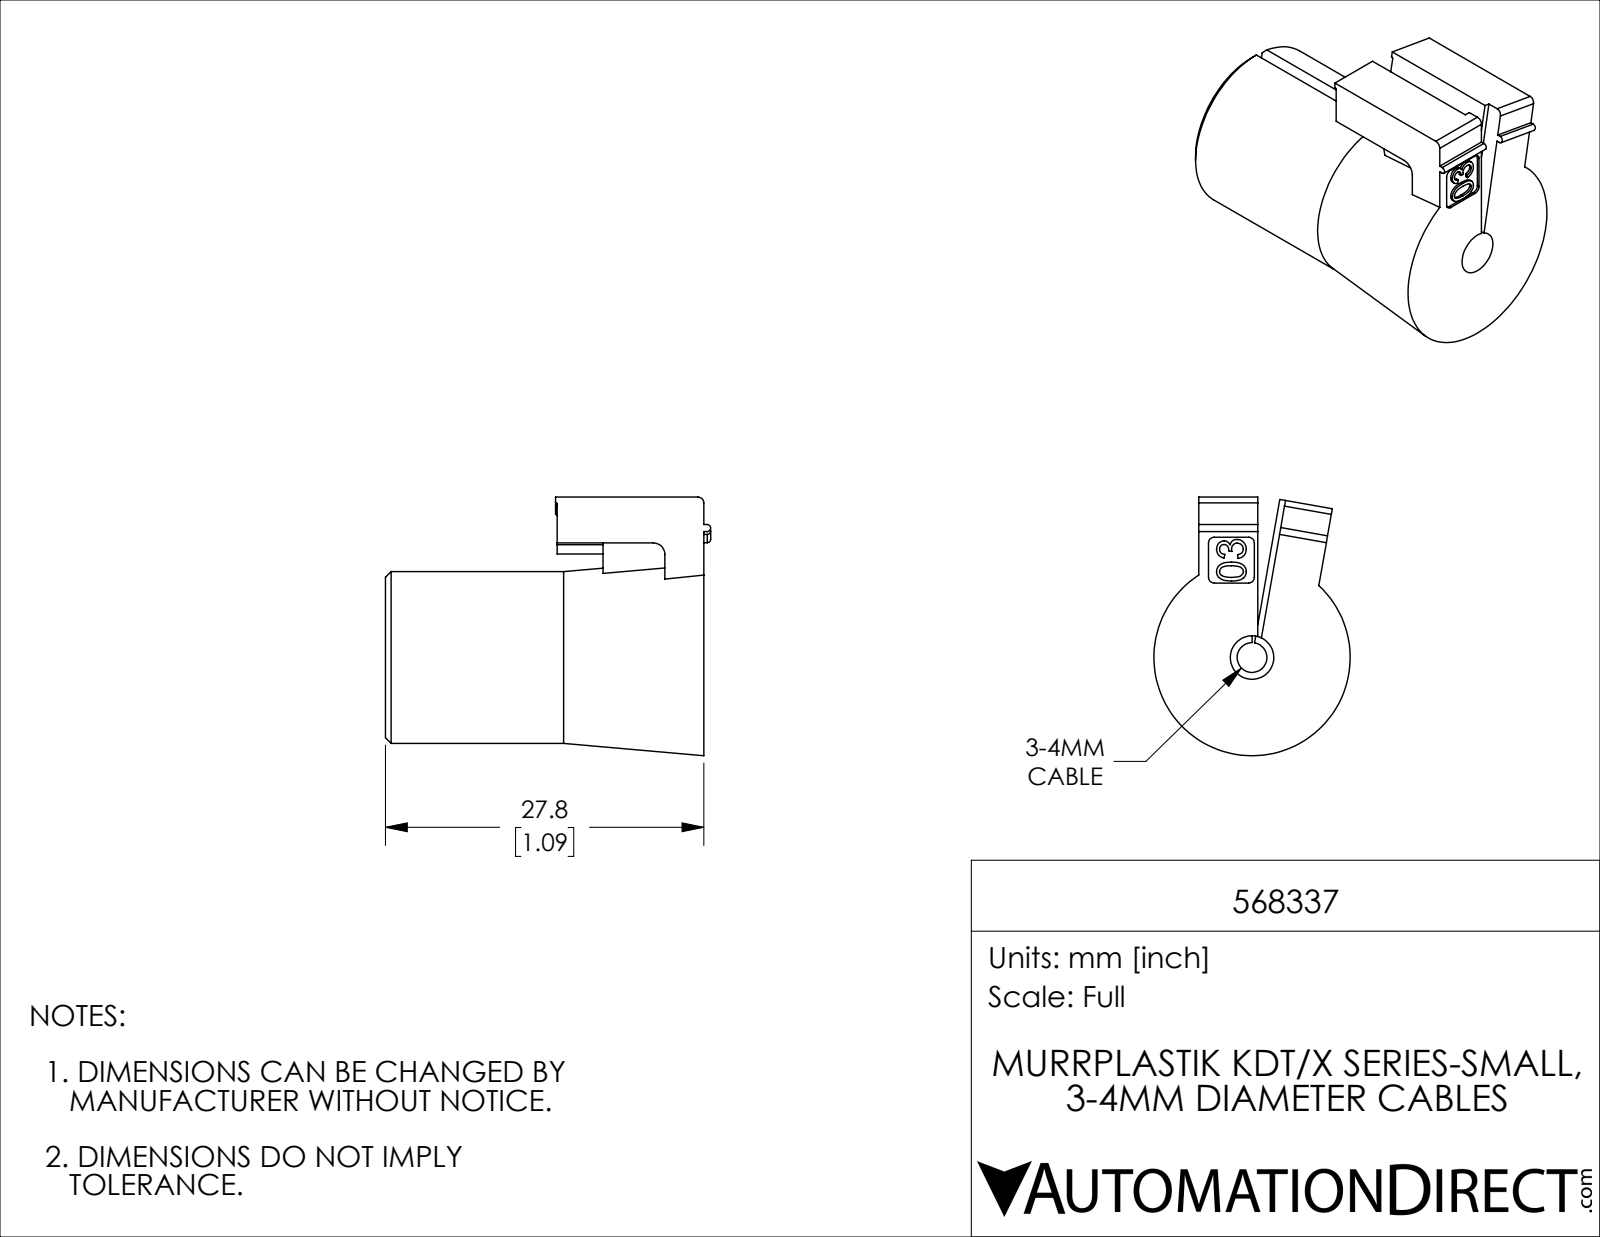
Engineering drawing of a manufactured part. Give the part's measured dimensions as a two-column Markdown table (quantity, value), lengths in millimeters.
| quantity | value |
| --- | --- |
| part name | 568337 |
| STEP written by | SolidWorks 2019 (CONFIG_CONTROL_DESIGN) |
| units | millimeters |
| bodies | 1 solid, 111 faces (49 planar, 24 cylindrical, 38 other) |
| overall size | 28.4 × 22.6 × 17.1 |
| volume | 5 390 mm³ |
| surface area | 2 867 mm² |
| round holes (diameter × count) | 2.6 × 1, 3.8 × 1 |
| round bosses / shafts (diameter × count) | 15 × 1 |
| partial cylindrical surfaces (radius × count) | 0.5 × 6, 0.1 × 2, 0.3 × 2, 1 × 2 |
| main face-to-face distances | 27.8, 4.6, 4, 0.5, 12.8, 15, 4.1, 5.2, 8.8, 19 |
